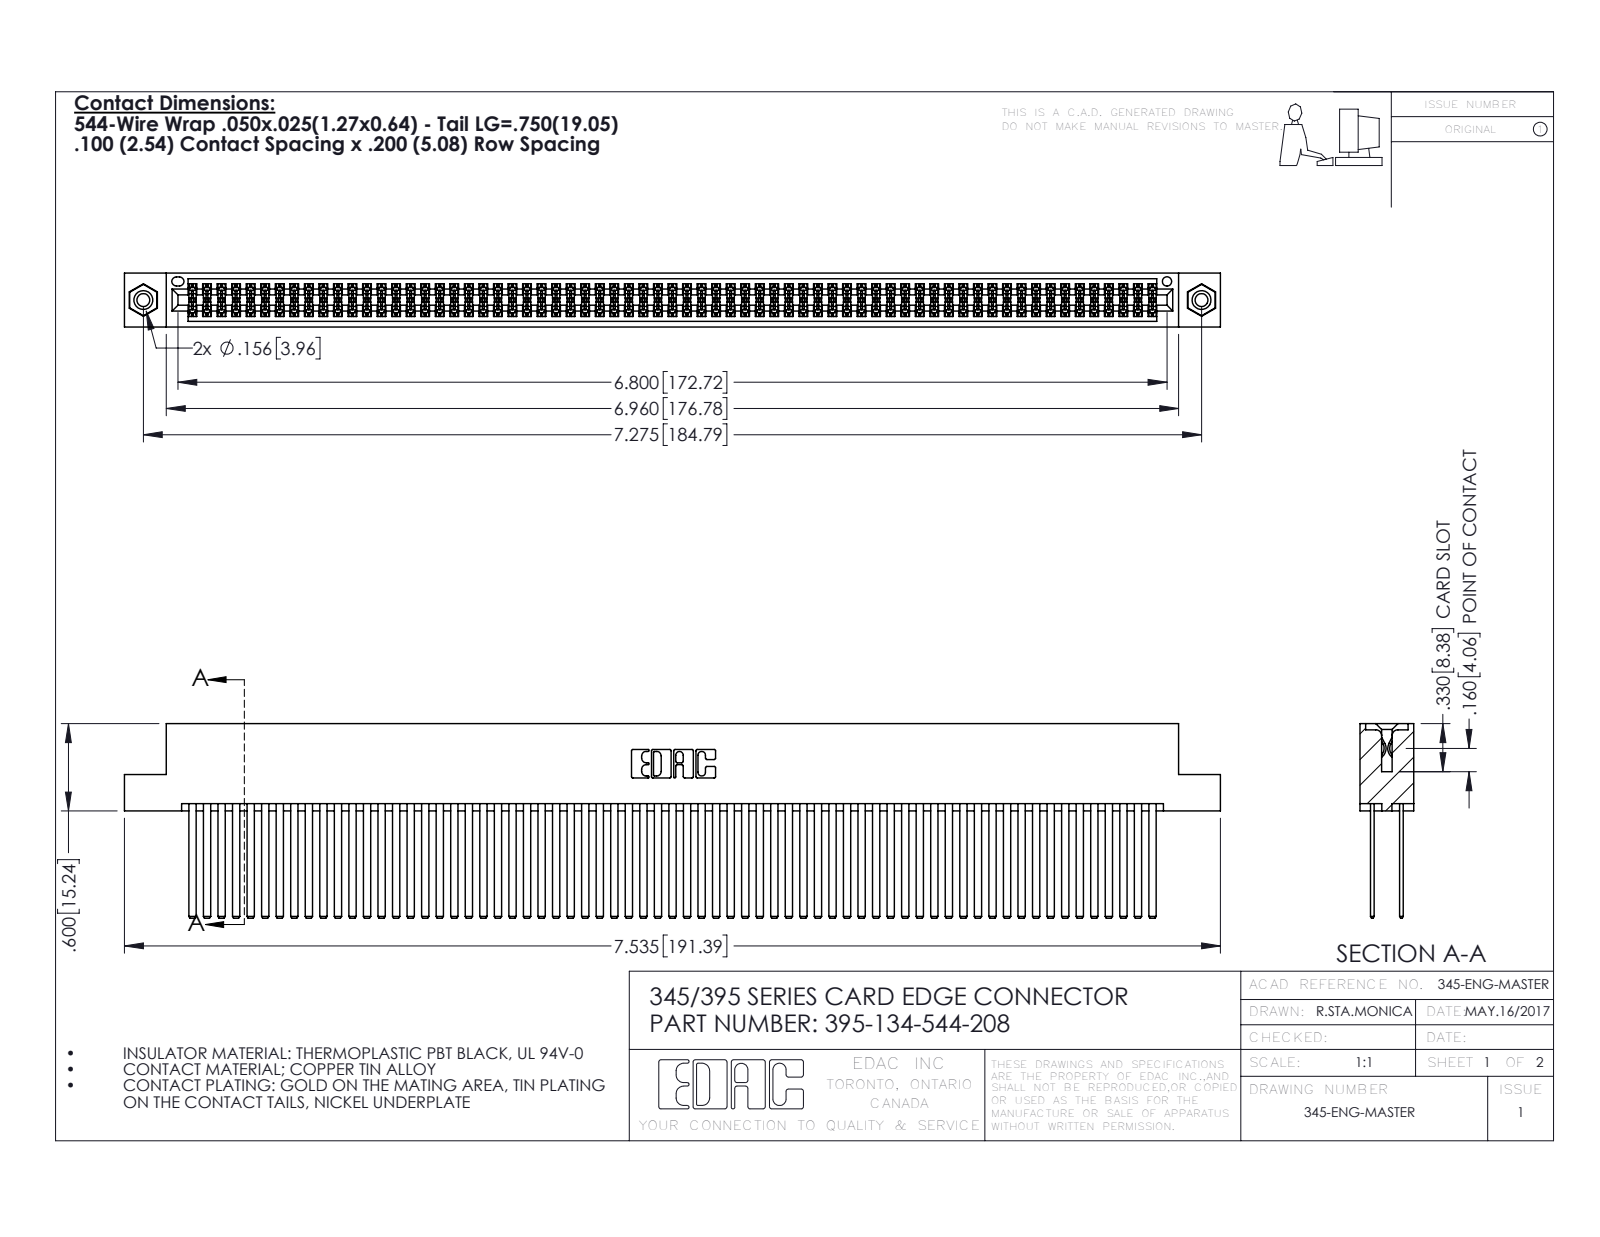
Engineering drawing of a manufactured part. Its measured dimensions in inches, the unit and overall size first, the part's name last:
Units: inches
Overall size (bounding box): 7.535 × 1.337 × 0.37
Round holes (diameter × count): ⌀0.089 ×2, ⌀0.125 ×2, ⌀0.156 ×2, ⌀0.064 ×1
Round bosses / shafts (diameter × count): ⌀0.155 ×2
Partial cylindrical surfaces — rounded edges, fillets, slot ends (radius × count): R0.006 ×201, R0.01 ×22, R0.007 ×6, R0.031 ×6, R0.026 ×3, R0.014 ×2, R0.019 ×2, R0.022 ×2
Main face-to-face distances: 0.2, 0.025, 0.072, 0.098, 0.272, 0.298, 0.225, 0.175, 0.37, 0.05
Hole centre spacings: 0.27, 7.039, 7.275
Volume: 1.263 in³ · Surface area: 56.72 in²
Bodies: 137 solids, 6082 faces (3998 planar, 2068 cylindrical, 16 other)
Part name (STEP PRODUCT): 345-292-001_345-293-144; 345-250-001_345-250-003-102; 395-134-544-208; 345 Part_Flush Mounting Lugs - 0.156 Dia-TI
STEP written by: SolidWorks 2016 (CONFIG_CONTROL_DESIGN)
